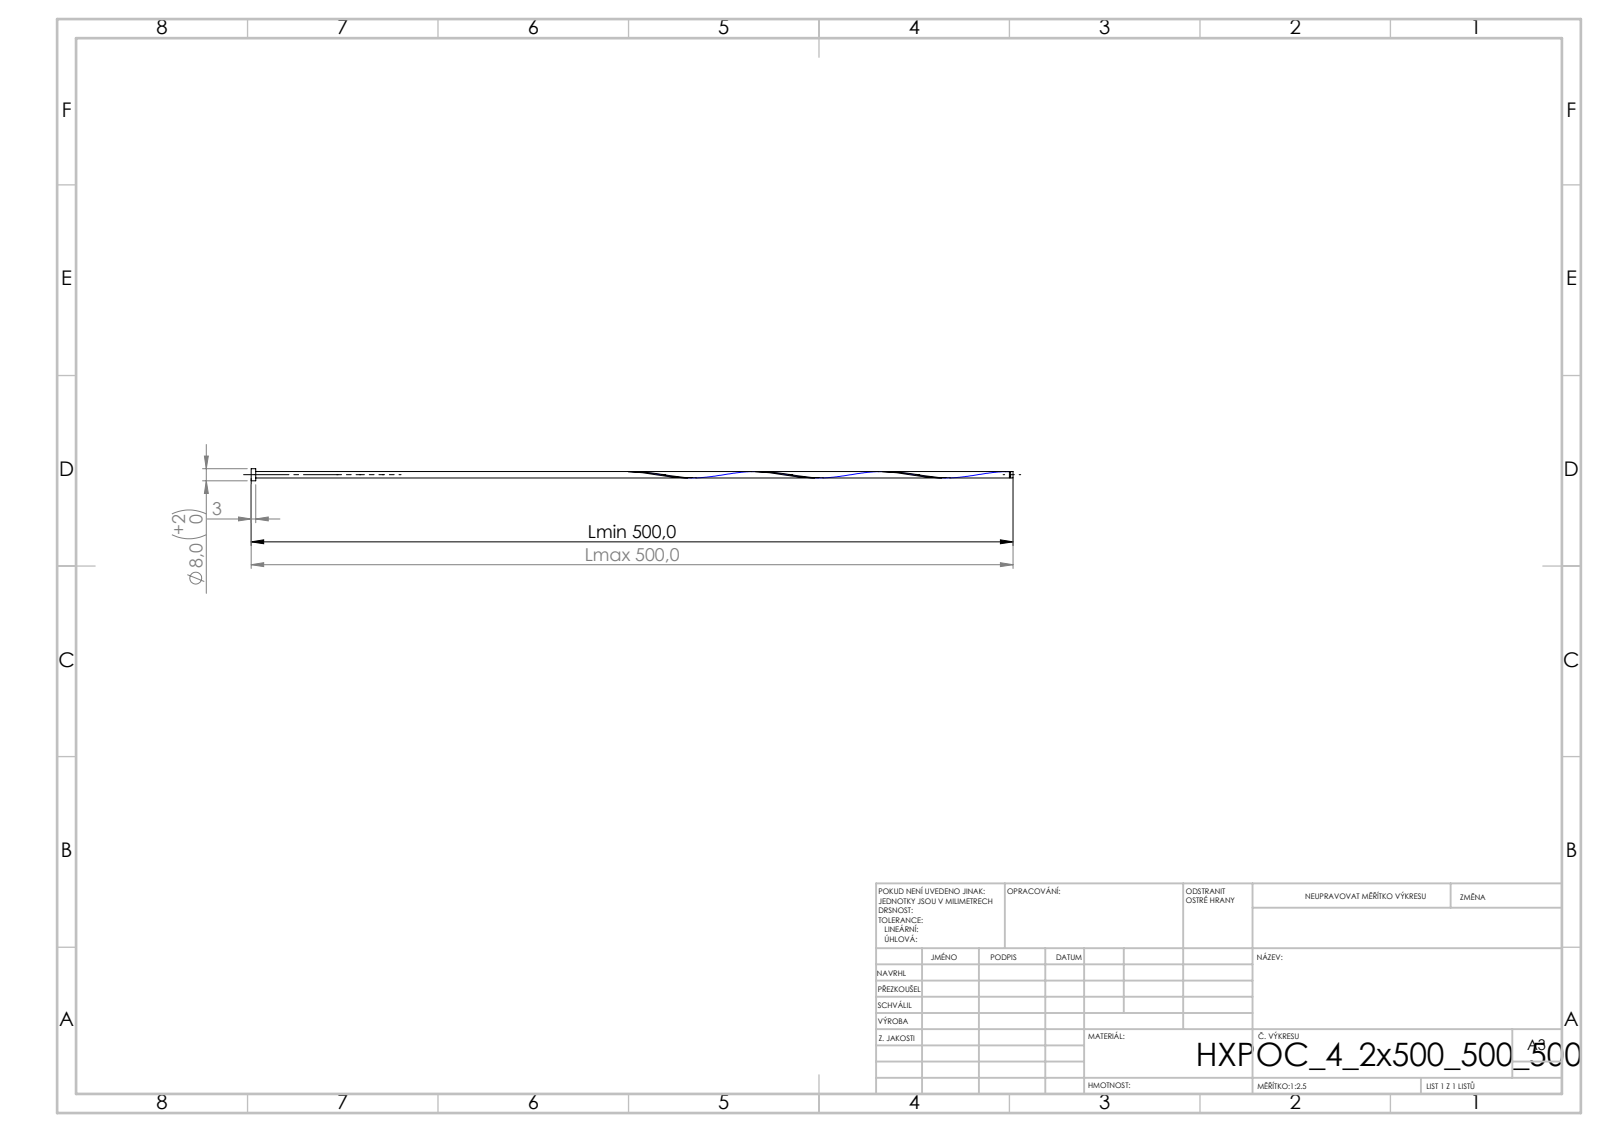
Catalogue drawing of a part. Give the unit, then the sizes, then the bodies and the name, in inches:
Units: inches
Overall size (bounding box): 19.685 × 0.315 × 0.315
Round bosses / shafts (diameter × count): ⌀0.315 ×1, ⌀0.165 ×1, ⌀0.132 ×1
Main face-to-face distances: 0.118, 19.685, 19.567, 19.624, 19.506, 0.061, 19.591, 19.472, 0.033, 0.094
Volume: 0.519 in³ · Surface area: 14.01 in²
Bodies: 1 solid, 16 faces (6 planar, 9 cylindrical, 1 other)
STEP written by: SolidWorks 2019 (CONFIG_CONTROL_DESIGN)
